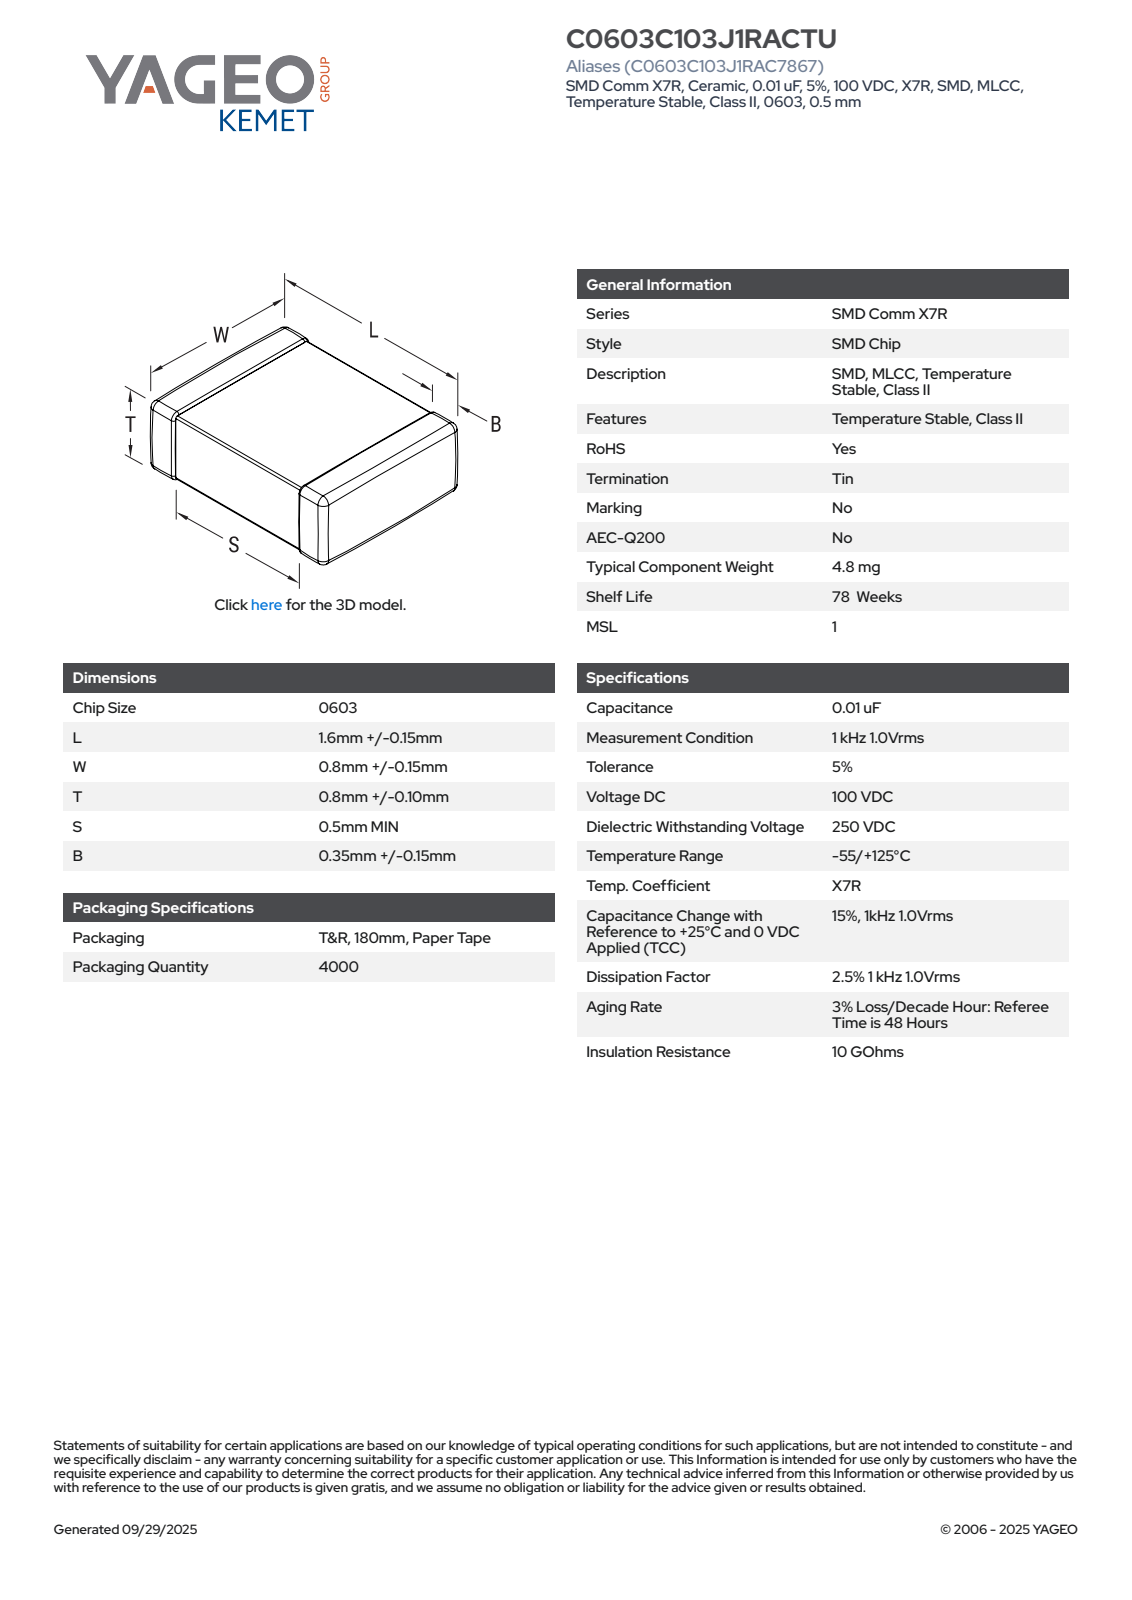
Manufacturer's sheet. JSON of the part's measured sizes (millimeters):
{"part_name": "CCS_CCSTD_0603_L1.75W0.95T0.9B0.35", "step_written_by": "SolidWorks 2014 (AUTOMOTIVE_DESIGN)", "units": "millimeters", "bodies": {"solids": 4, "faces": 125, "planar": 71, "cylindrical": 38, "other": 16}, "overall_size": [1.75, 0.95, 0.9], "volume_mm3": 1, "surface_area_mm2": 8, "face_to_face_distances": [0.88, 0.93, 0.86, 0.91, 1.75, 0.9, 0.95, 0.89, 0.87, 0.81]}
